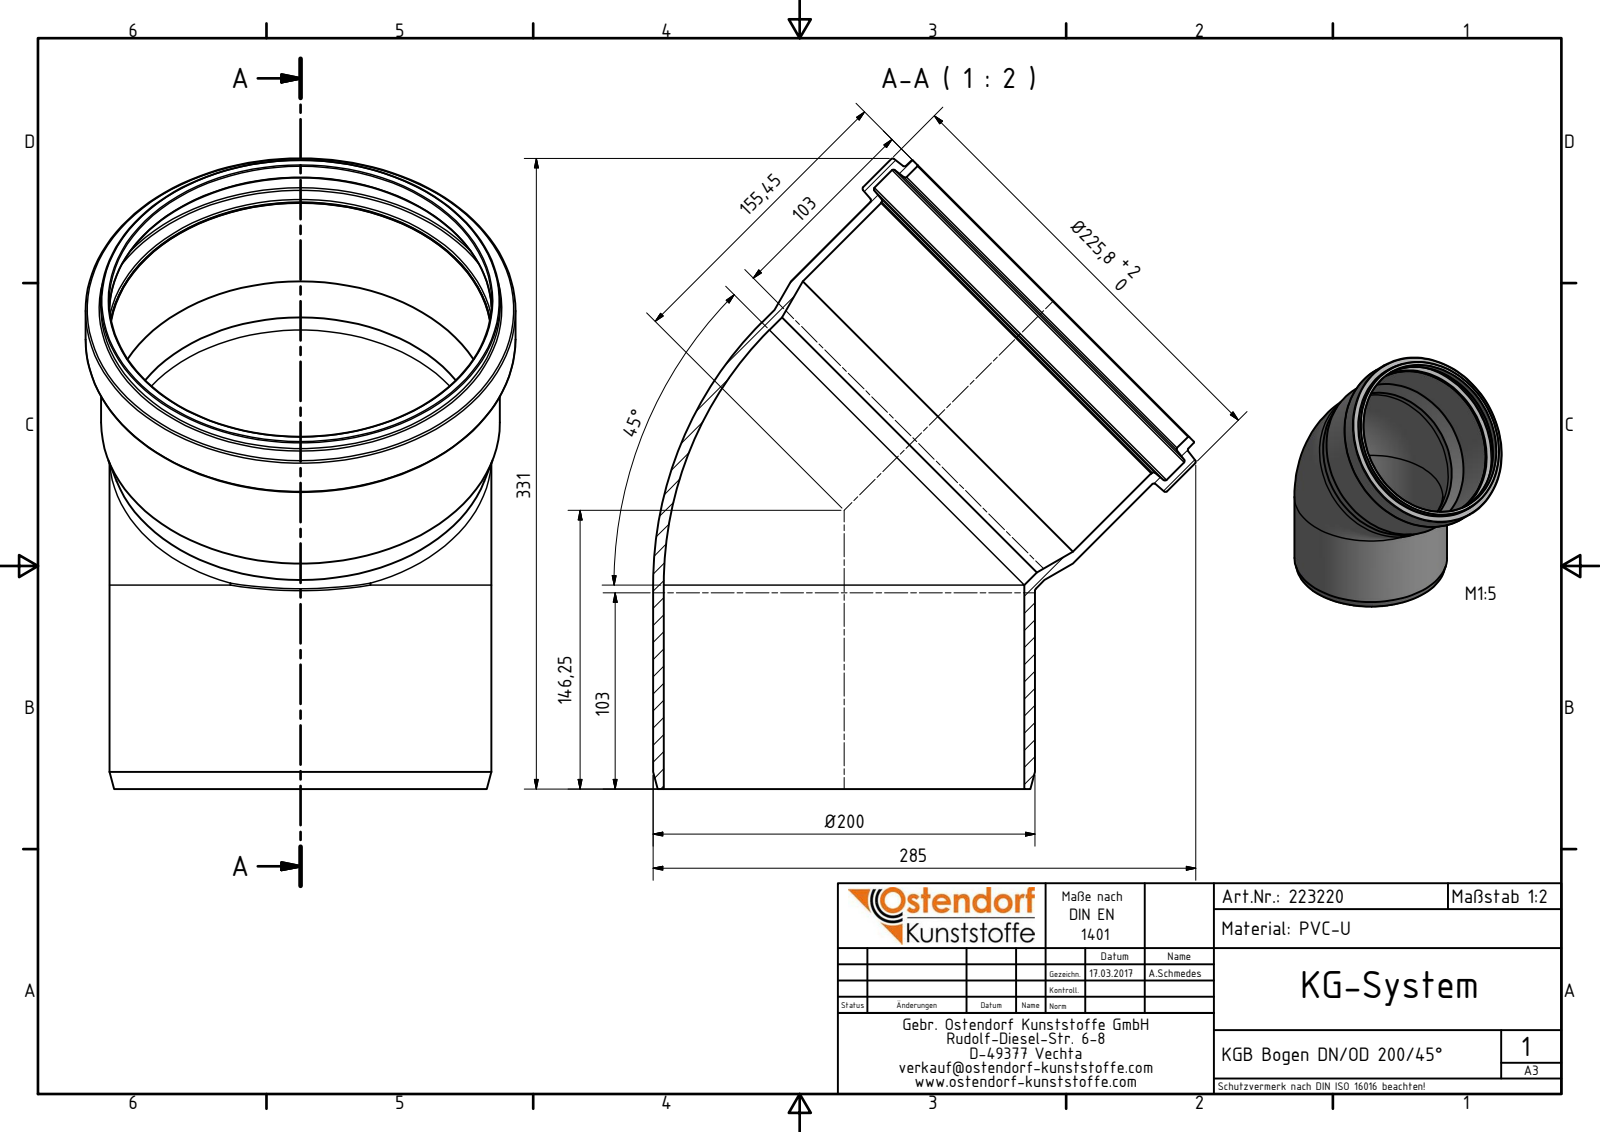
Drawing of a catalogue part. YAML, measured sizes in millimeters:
part_name: "223220 KGB Bogen DN_OD 200_45°"
step_written_by: "Autodesk Inventor 2016 (AUTOMOTIVE_DESIGN)"
units: millimeters
bodies: {solids: 1, faces: 34, planar: 3, cylindrical: 11, other: 20}
overall_size: [331, 285, 225.8]
volume: 936965
surface_area: 396167
round_holes:
  - {diameter: 189.3, count: 2}
  - {diameter: 200.9, count: 2}
  - {diameter: 200.6, count: 1}
  - {diameter: 217, count: 1}
round_bosses_or_shafts:
  - {diameter: 200.5, count: 2}
  - {diameter: 225.8, count: 1}
  - {diameter: 209.7, count: 1}
  - {diameter: 209.4, count: 1}
face_to_face_distances: [27.56]
